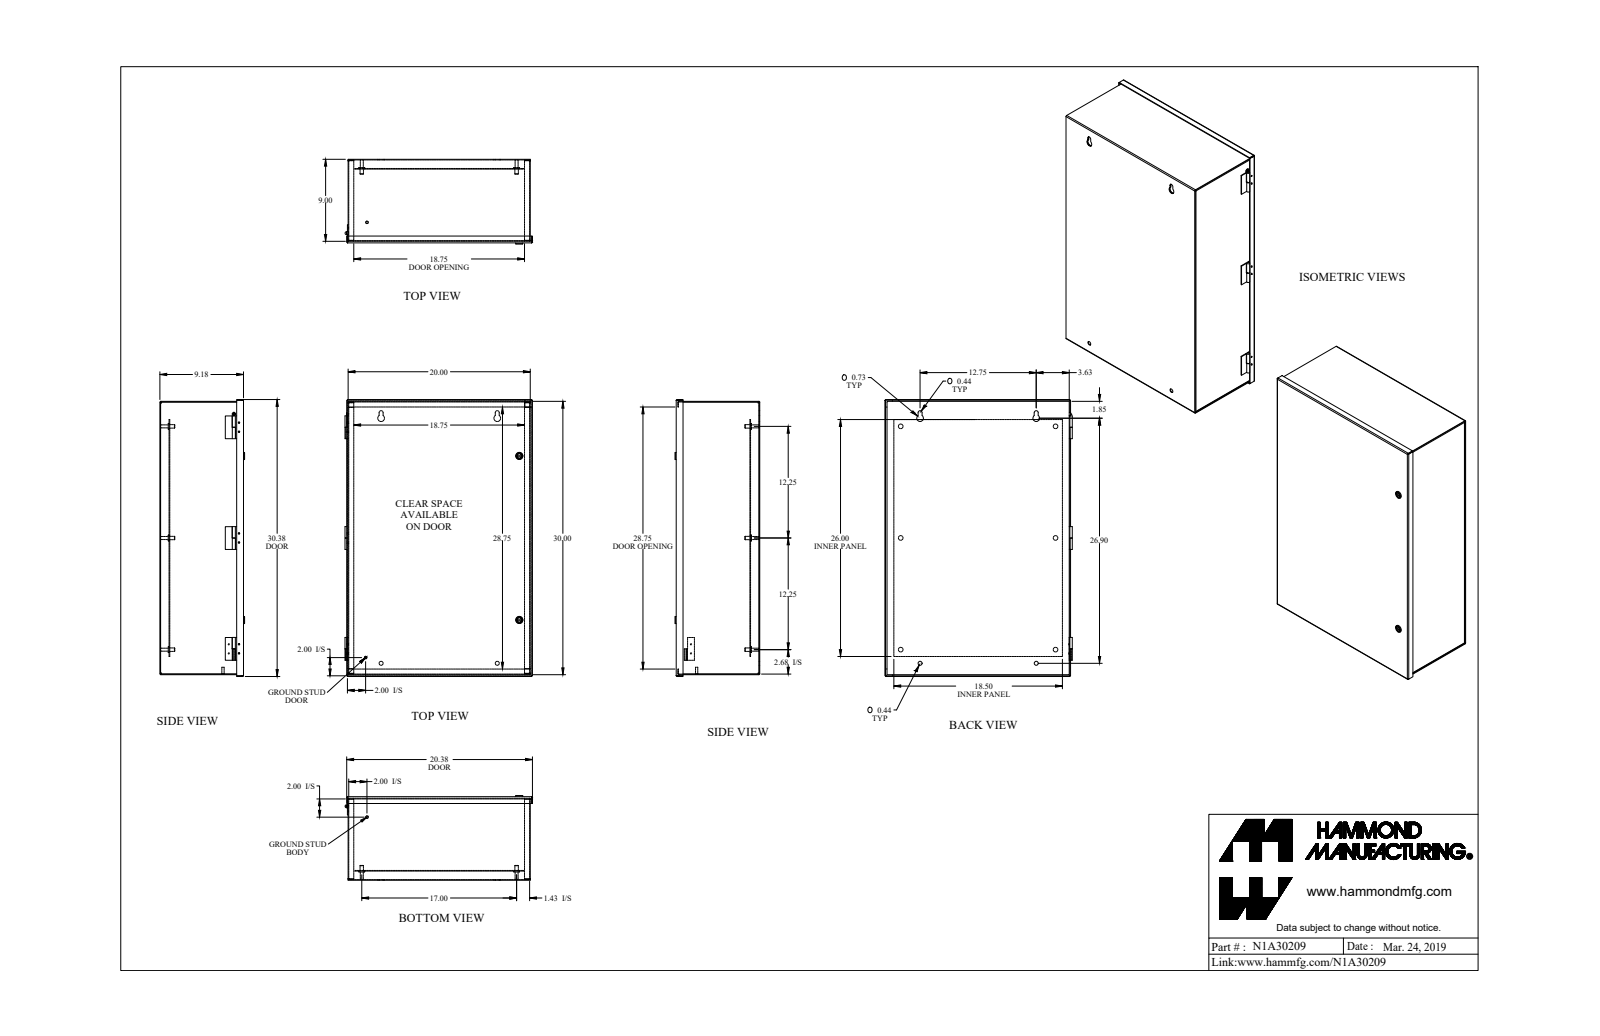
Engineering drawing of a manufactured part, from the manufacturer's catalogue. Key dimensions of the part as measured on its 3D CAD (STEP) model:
Part name (STEP PRODUCT): N1A30209
STEP written by: SolidWorks 2018 (AUTOMOTIVE_DESIGN)
Units: inches
Bodies: 34 solids, 767 faces (434 planar, 269 cylindrical, 64 other)
Overall size (bounding box): 30.384 × 20.574 × 9.299
Volume: 202.6 in³ · Surface area: 5 639 in²
Round holes (diameter × count): ⌀0.14 ×12, ⌀0.5 ×6, ⌀0.307 ×4, ⌀0.445 ×4, ⌀0.734 ×3, ⌀0.437 ×2, ⌀0.516 ×2, ⌀0.17 ×1, ⌀0.187 ×1
Round bosses / shafts (diameter × count): ⌀0.128 ×12, ⌀0.375 ×7, ⌀0.65 ×6, ⌀0.33 ×6, ⌀1 ×4, ⌀0.788 ×2, ⌀0.535 ×2, ⌀0.496 ×2
Partial cylindrical surfaces — rounded edges, fillets, slot ends (radius × count): R0.036 ×16, R0.108 ×16, R0.219 ×3, R0.06 ×2, R0.125 ×2, R0.153 ×2, R0.315 ×2, R0.03 ×1
Main face-to-face distances: 0.072, 9.105, 1.009, 8.096, 9.033, 9.177, 19.928, 0.937, 1.081, 8.024
Hole centre spacings: 1, 1.119, 12.156, 12.157, 12.25, 20.954, 13.319, 17
